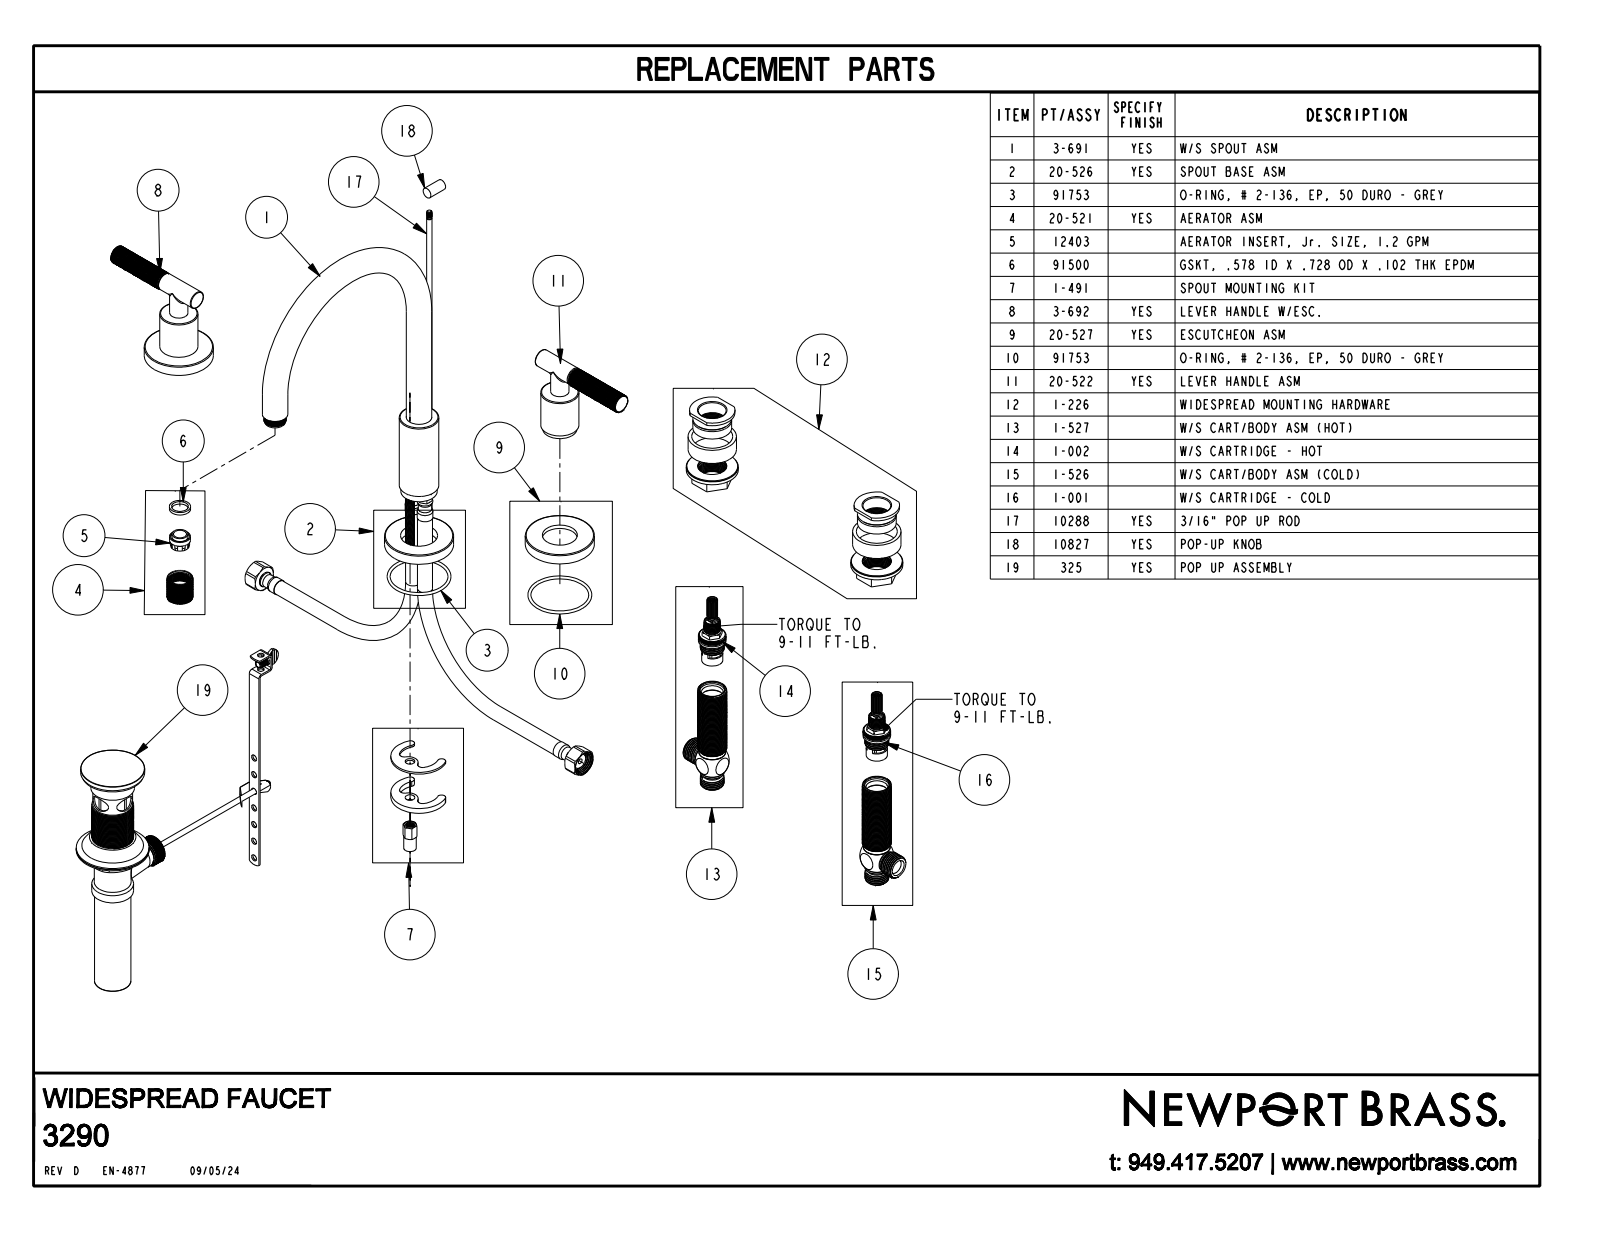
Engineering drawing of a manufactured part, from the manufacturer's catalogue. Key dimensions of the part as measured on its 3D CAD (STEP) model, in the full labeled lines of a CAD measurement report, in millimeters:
Part name (STEP PRODUCT): 3290
STEP written by: CREO PARAMETRIC BY PTC INC, 2018400 (CONFIG_CONTROL_DESIGN)
Units: millimetres
Bodies: 3 solids, 19753 faces (150 planar, 3883 cylindrical, 15720 other)
Overall size (bounding box): 355.6 × 295.1 × 222.3
Volume: 423 600 mm³ · Surface area: 85 810 mm²
Round holes (diameter × count): ⌀13.6 ×2, ⌀14.2 ×1, ⌀15.7 ×1, ⌀17.6 ×1
Round bosses / shafts (diameter × count): ⌀60.3 ×3, ⌀16 ×3, ⌀33.4 ×2, ⌀31.8 ×2, ⌀22.2 ×2, ⌀13 ×2, ⌀34.5 ×1, ⌀33.8 ×1
Partial cylindrical surfaces — rounded edges, fillets, slot ends (radius × count): R5 ×2, R8.6 ×1
Main face-to-face distances: 9.5, 45.1, 35.6, 82.6, 73, 37.5, 74, 84, 98.8, 172.8
Hole centre spacings: 207.6, 203.2
